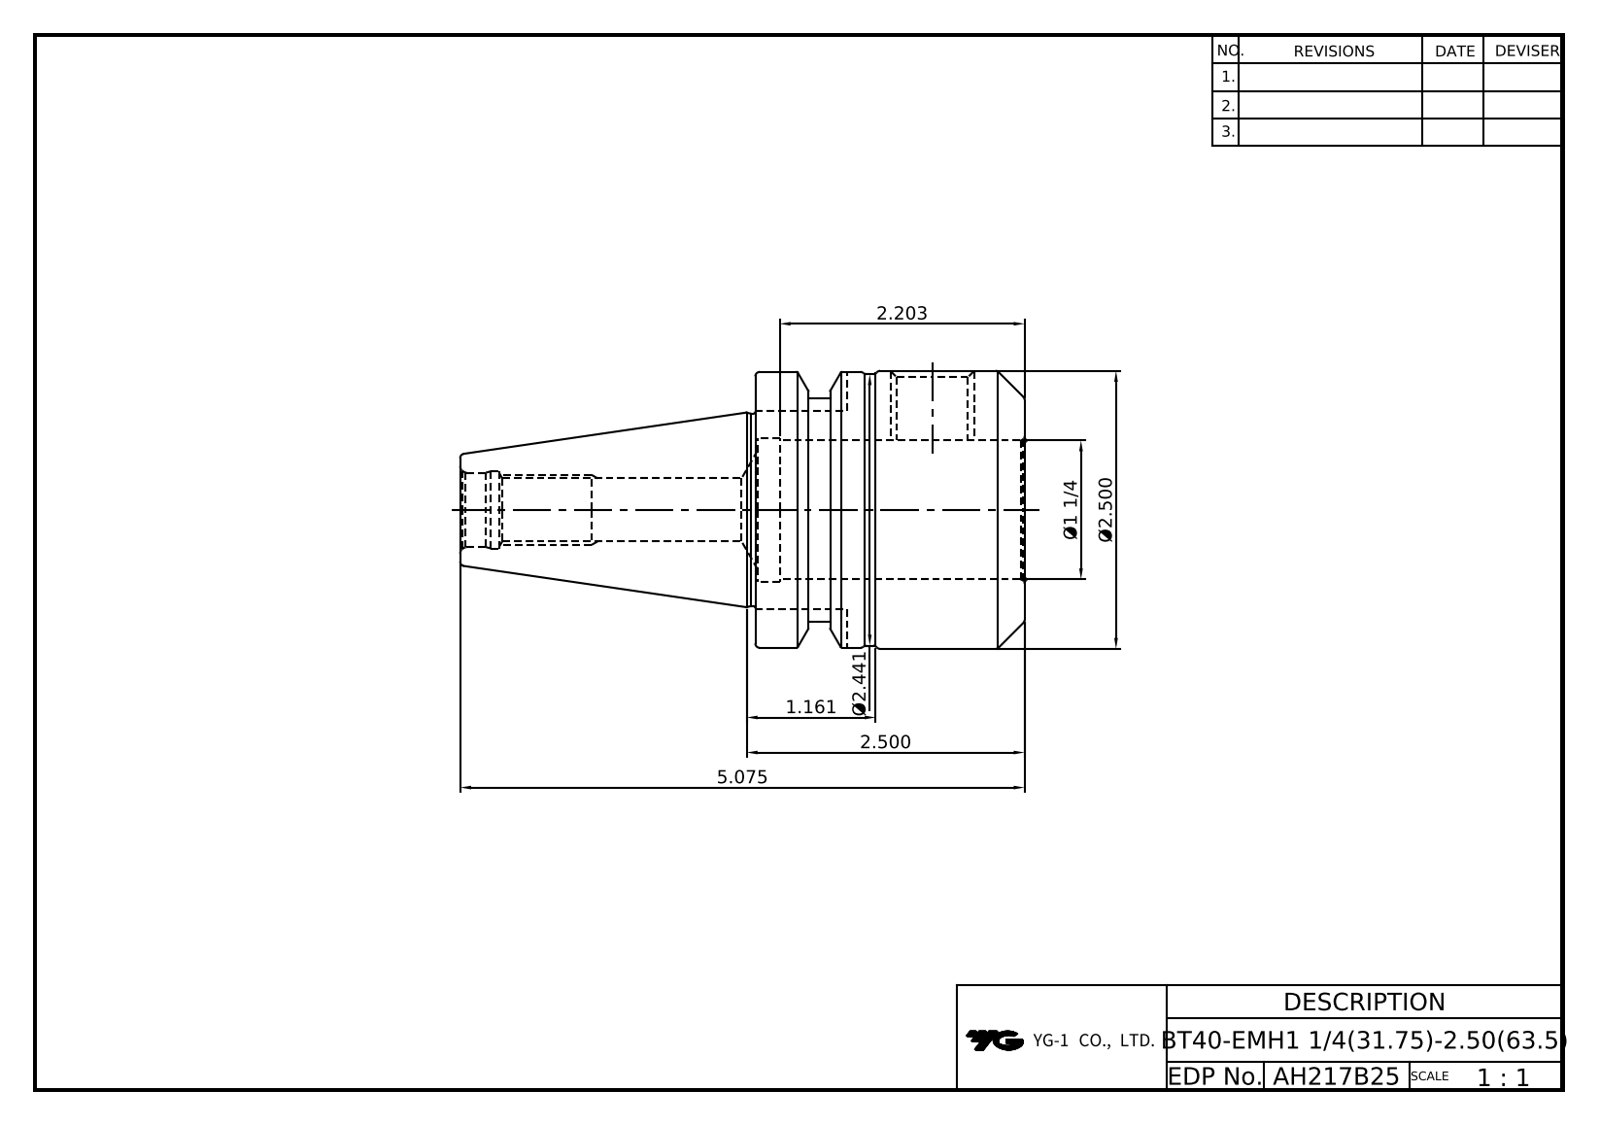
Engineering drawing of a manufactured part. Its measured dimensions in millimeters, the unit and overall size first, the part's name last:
Units: millimetres
Overall size (bounding box): 128.9 × 63.5 × 63.5
Round holes (diameter × count): ⌀13.5 ×1, ⌀13.84 ×1, ⌀17 ×1, ⌀17.32 ×1, ⌀17.6 ×1, ⌀31.75 ×1, ⌀32.95 ×1
Round bosses / shafts (diameter × count): ⌀63.5 ×1, ⌀63 ×1, ⌀62 ×1, ⌀52.6 ×1, ⌀44 ×1
Partial cylindrical surfaces — rounded edges, fillets, slot ends (radius × count): R8.05 ×1
Main face-to-face distances: 61.5, 45.2, 0.54, 60.96, 16.1, 5, 11.56, 67.4, 67.94, 128.9
Volume: 181 697 mm³ · Surface area: 34 565 mm²
Bodies: 1 solid, 58 faces (17 planar, 17 cylindrical, 24 other)
Part name (STEP PRODUCT): LO-BT40-EMH31.75-63.5
STEP written by: Autodesk Inventor 2022 (AUTOMOTIVE_DESIGN)
